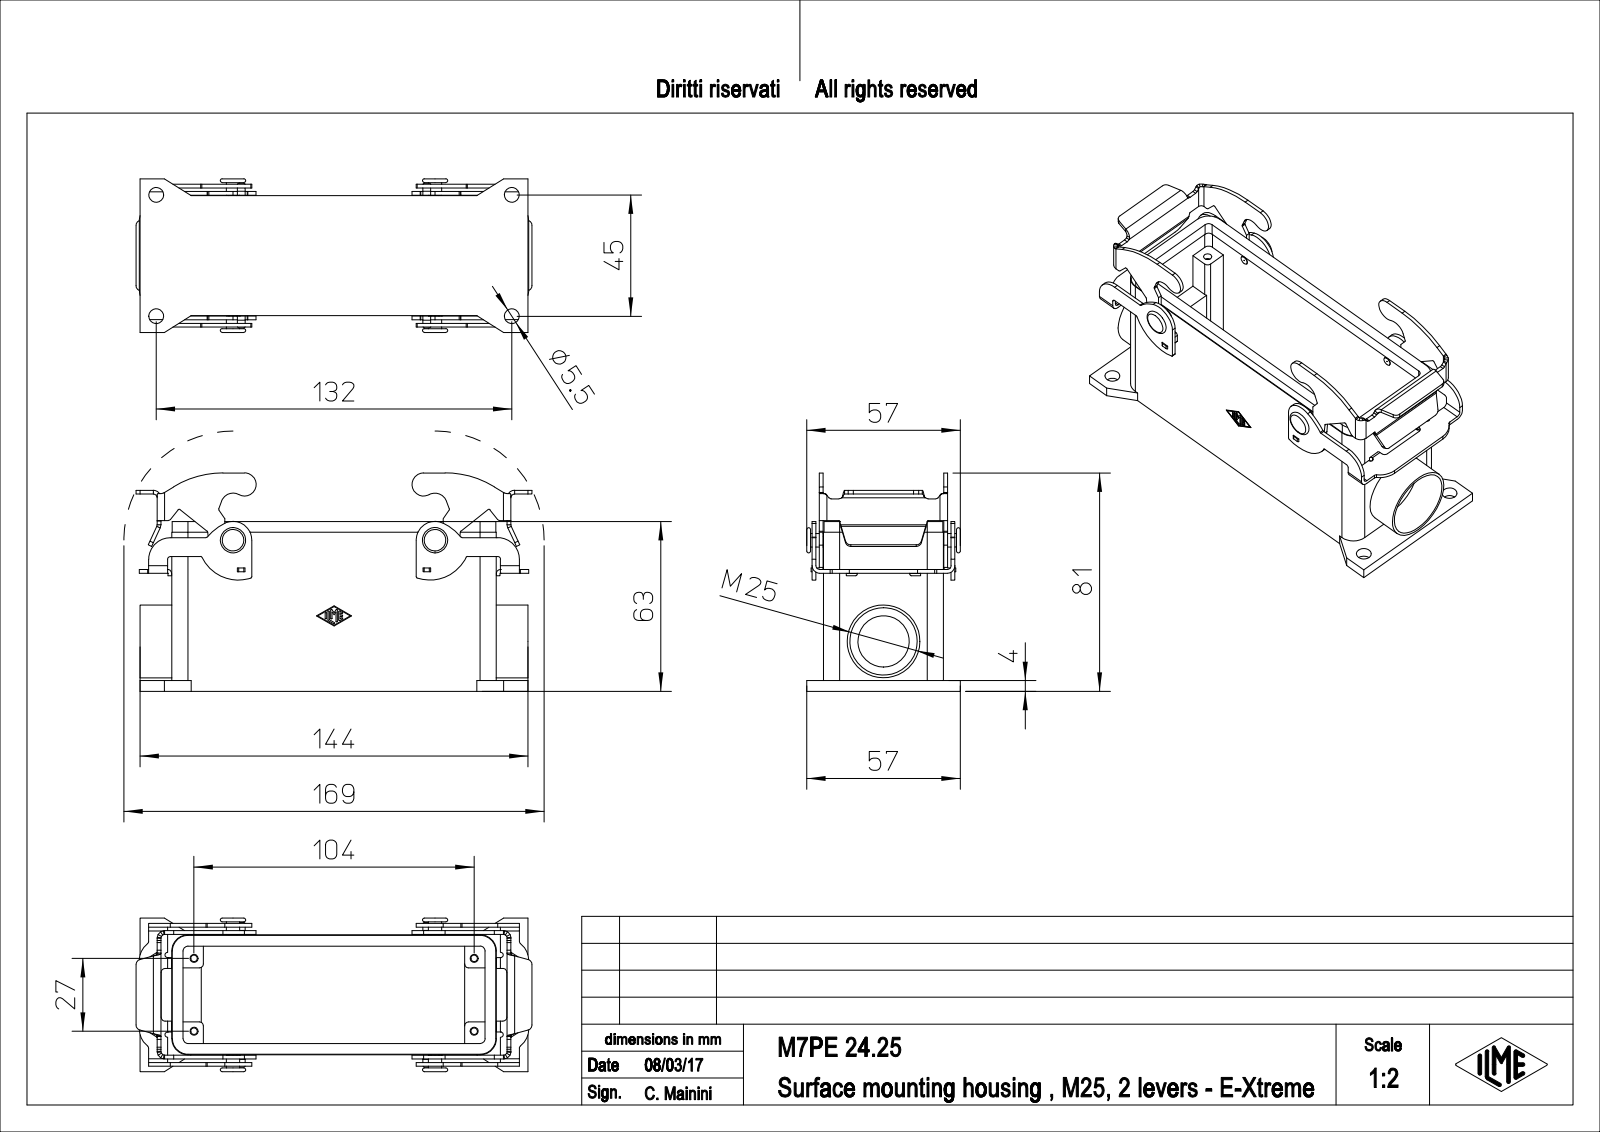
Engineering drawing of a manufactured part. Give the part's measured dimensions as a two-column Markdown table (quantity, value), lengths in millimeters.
| quantity | value |
| --- | --- |
| part name | M7PE_24.25 |
| STEP written by | PTC Creo Elements/Direct Modeling 19.0E 27-Jun-2016 (C) Parametric Technology GmbH (AUTOMOTIVE_DESIGN) |
| units | millimeters |
| bodies | 1 solid, 609 faces (293 planar, 270 cylindrical, 46 other) |
| overall size | 146.97 × 81 × 57 |
| volume | 125 970 mm³ |
| surface area | 72 538 mm² |
| round holes (diameter × count) | 2.46 × 4, 3 × 4, 5.5 × 4, 3.5 × 2, 19 × 1, 25 × 1 |
| round bosses / shafts (diameter × count) | 5 × 2, 3.2 × 2, 3 × 2, 27 × 1 |
| partial cylindrical surfaces (radius × count) | 0.5 × 22, 1 × 18, 0.25 × 16, 1.5 × 14, 2 × 12, 1.4 × 10, 2.8 × 10, 8 × 6 |
| main face-to-face distances | 4, 40.5, 1.4, 44.5, 36.5, 2.7, 48.9, 8.25, 11.75, 4.15 |
| hole center spacings | 16.64, 38.63, 118.34, 123.37, 27, 45, 104, 107.45 |
